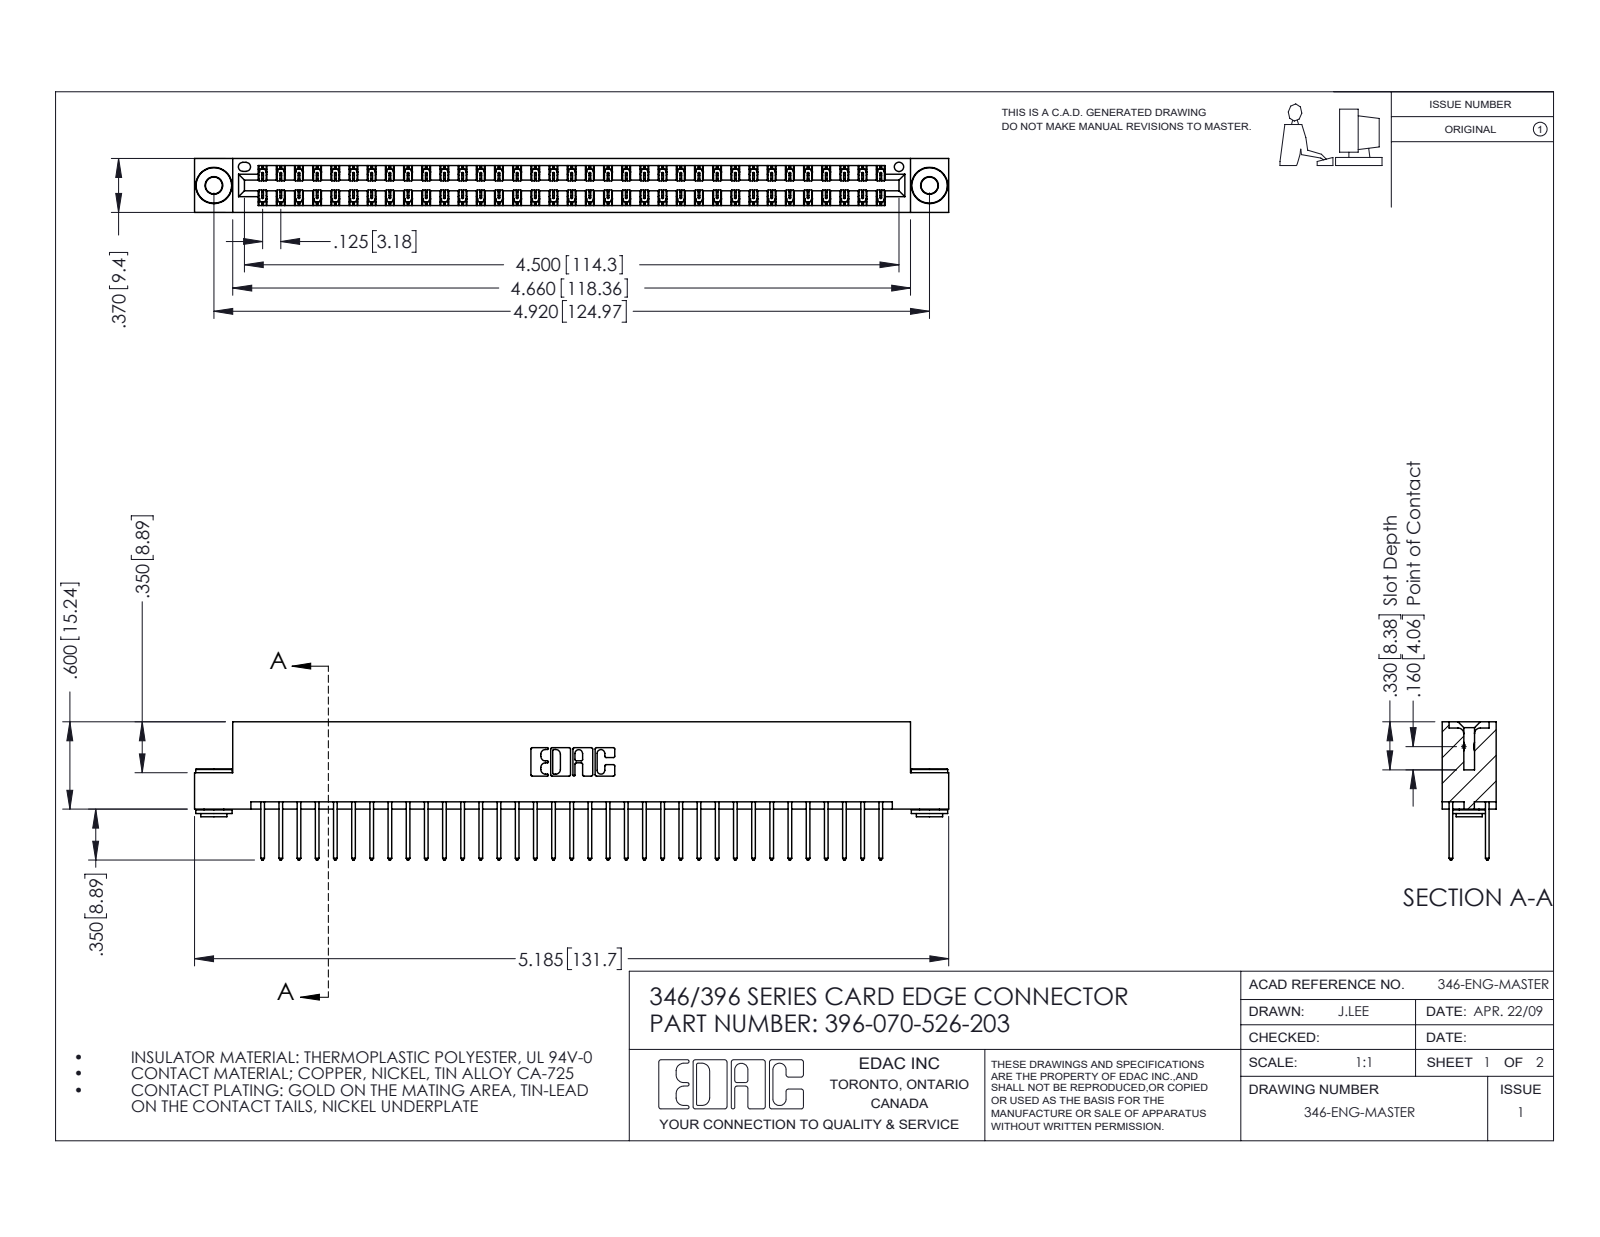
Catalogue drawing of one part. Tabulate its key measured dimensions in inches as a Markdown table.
| quantity | value |
| --- | --- |
| part name | 346 Part_Flush Mounting Lugs - 0.156 Dia-TH; 345-250-002_345-250-002-102; 396-070-526-203; 345-292-001_345-293-126 |
| STEP written by | SolidWorks 2016 (CONFIG_CONTROL_DESIGN) |
| units | inches |
| bodies | 73 solids, 3800 faces (2536 planar, 1256 cylindrical, 8 other) |
| overall size | 5.185 × 0.95 × 0.37 |
| volume | 0.789 in³ |
| surface area | 28.49 in² |
| round holes (diameter × count) | 0.116 × 2, 0.156 × 2, 0.064 × 1 |
| round bosses / shafts (diameter × count) | 0.25 × 2, 0.18 × 2, 0.136 × 2 |
| partial cylindrical surfaces (radius × count) | 0.006 × 105, 0.01 × 70, 0.01 × 22, 0.007 × 6, 0.031 × 6, 0.026 × 3, 0.014 × 2, 0.022 × 2 |
| main face-to-face distances | 0.048, 0.322, 0.25, 0.37, 0.025, 0.072, 0.298, 0.275, 0.148, 0.222 |
| hole center spacings | 0.246, 4.711, 4.92 |
